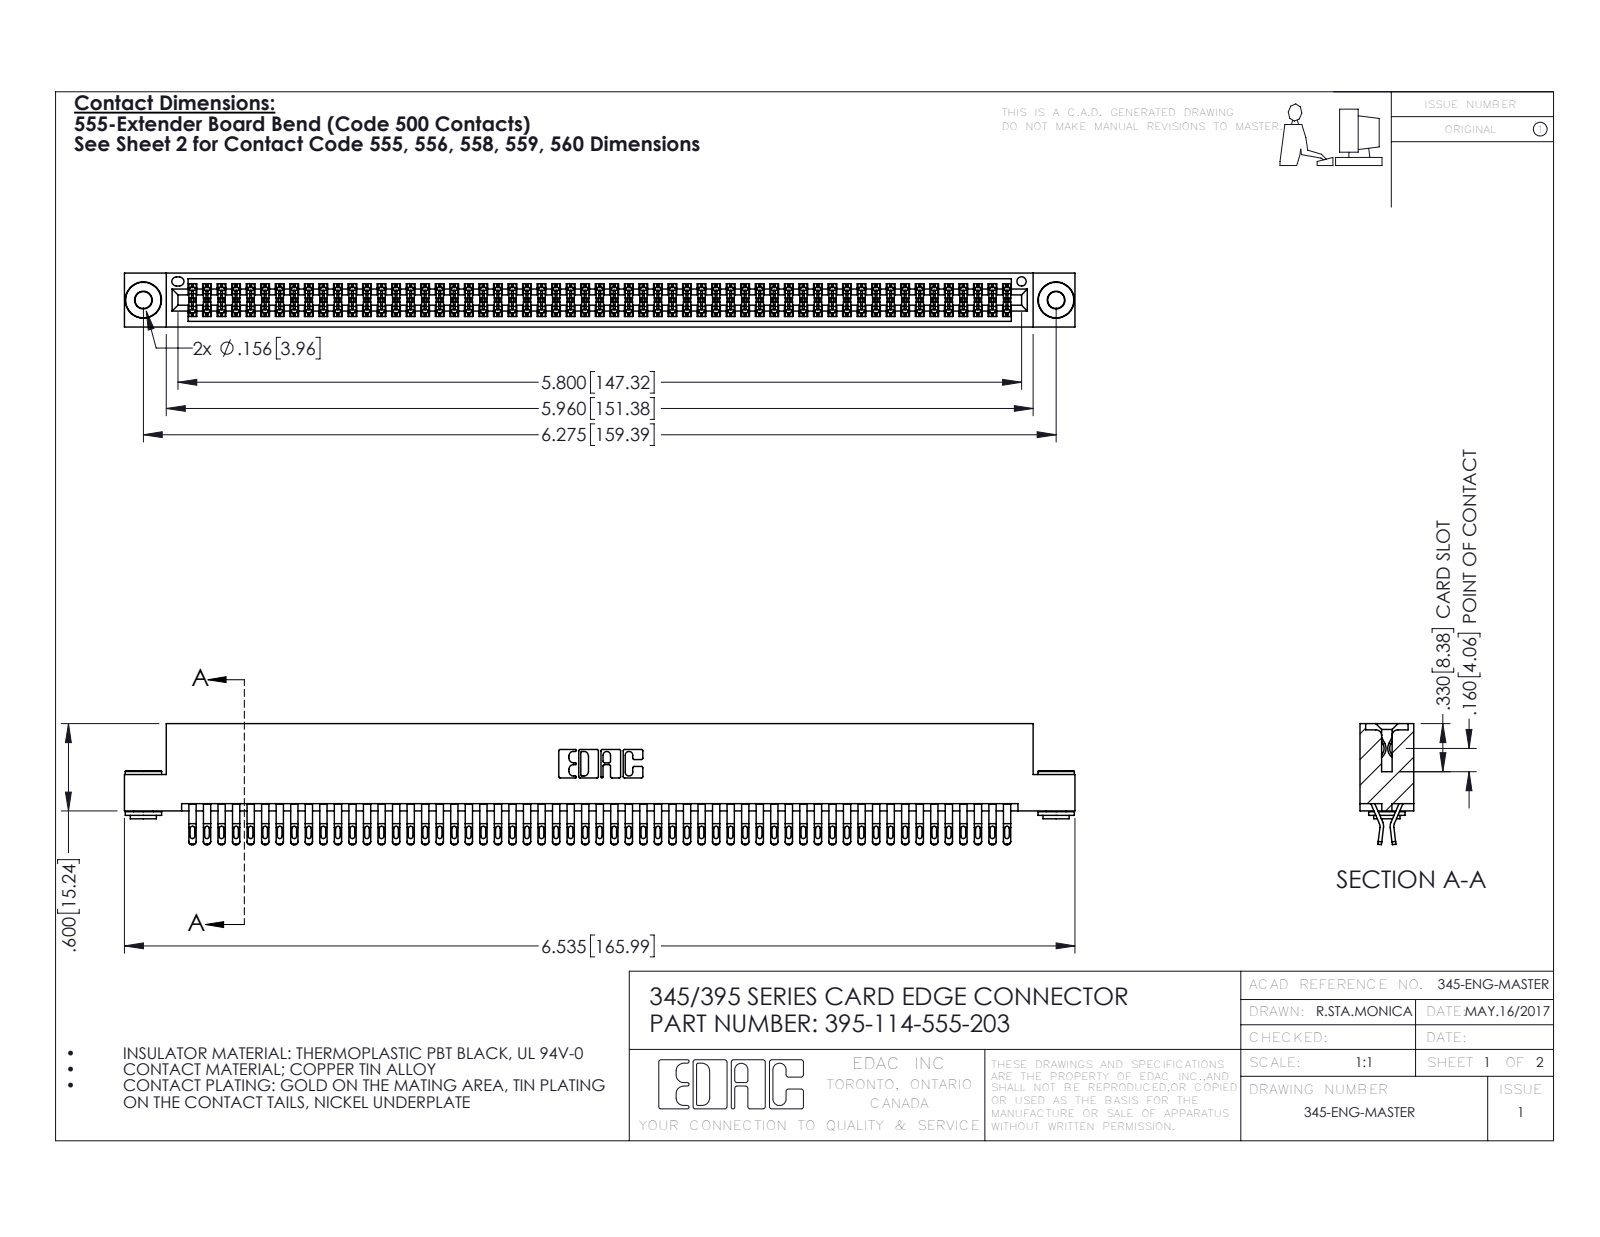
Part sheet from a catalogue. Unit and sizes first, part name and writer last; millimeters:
Units: millimetres
Overall size (bounding box): 166 × 21.1 × 9.4
Round holes (diameter × count): ⌀2.9 ×2, ⌀4 ×2, ⌀1.6 ×1
Round bosses / shafts (diameter × count): ⌀6.4 ×2, ⌀4.6 ×2, ⌀3.5 ×2
Partial cylindrical surfaces — rounded edges, fillets, slot ends (radius × count): R0.4 ×285, R0.5 ×228, R0.2 ×171, R0.3 ×22, R0.2 ×6, R0.8 ×6, R0.7 ×3, R0.3 ×2
Main face-to-face distances: 1.8, 7.6, 0.6, 9.4, 5.1, 2.5, 6.9, 5.7, 4.4, 3.8
Hole centre spacings: 6.9, 153.4, 159.4
Volume: 16 620 mm³ · Surface area: 26 210 mm²
Bodies: 117 solids, 6548 faces (3624 planar, 2916 cylindrical, 8 other)
Part name (STEP PRODUCT): 395-114-555-203; 345-292-001_555 Tail; 345-250-002_345-250-002-102; 345 Part_Flush Mounting Lugs - 0.156 Dia-TH
STEP written by: SolidWorks 2016 (CONFIG_CONTROL_DESIGN)
